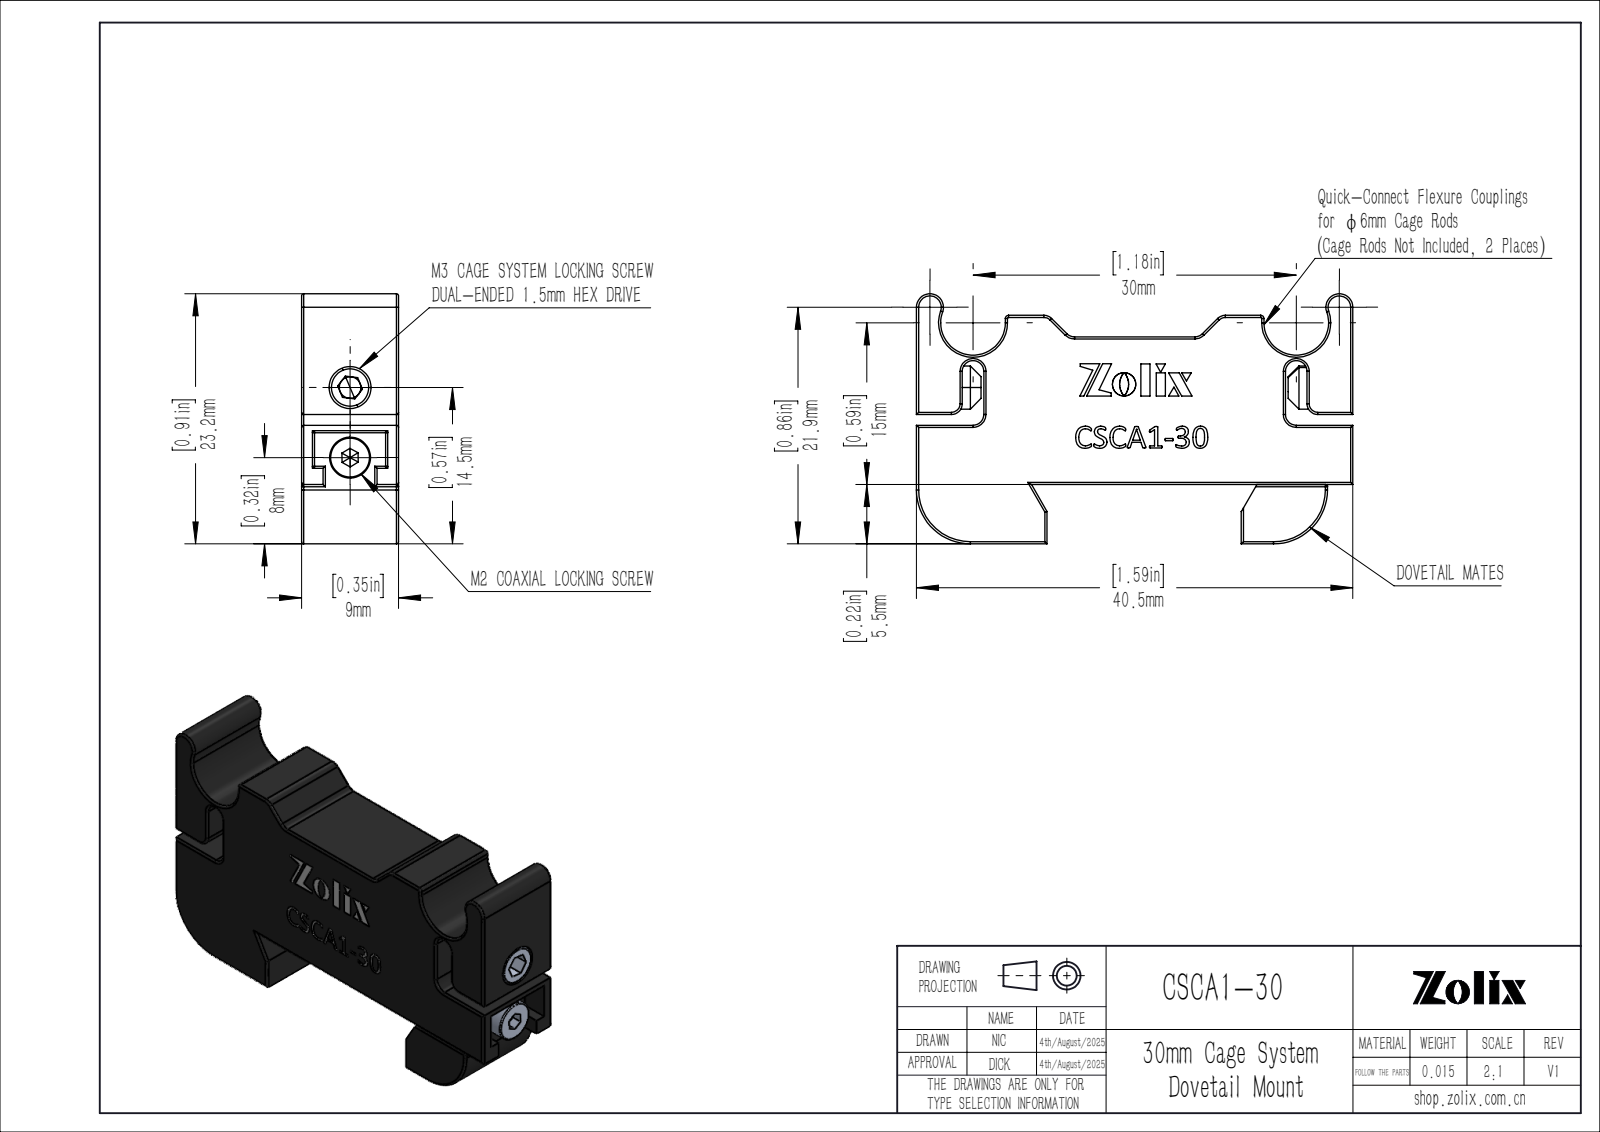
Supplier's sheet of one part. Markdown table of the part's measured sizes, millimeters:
| quantity | value |
| --- | --- |
| part name | CSCA1-30 |
| STEP written by | SolidWorks 2020 (CONFIG_CONTROL_DESIGN) |
| units | millimeters |
| bodies | 5 solids, 566 faces (296 planar, 114 cylindrical, 156 other) |
| overall size | 40.5 × 23.2 × 9 |
| volume | 5 640 mm³ |
| surface area | 3 870 mm² |
| round holes (diameter × count) | 1.6 × 1, 2.5 × 1, 3.3 × 1 |
| round bosses / shafts (diameter × count) | 4 × 1, 3.8 × 1, 2 × 1 |
| partial cylindrical surfaces (radius × count) | 0.2 × 60, 1 × 10, 0.3 × 2, 1.25 × 2, 2 × 2, 3 × 2, 5 × 1, 5 × 1 |
| main face-to-face distances | 9, 1, 5, 5.5, 2, 8, 7, 13.7, 8.7, 40.5 |
| hole center spacings | 6.5 |
